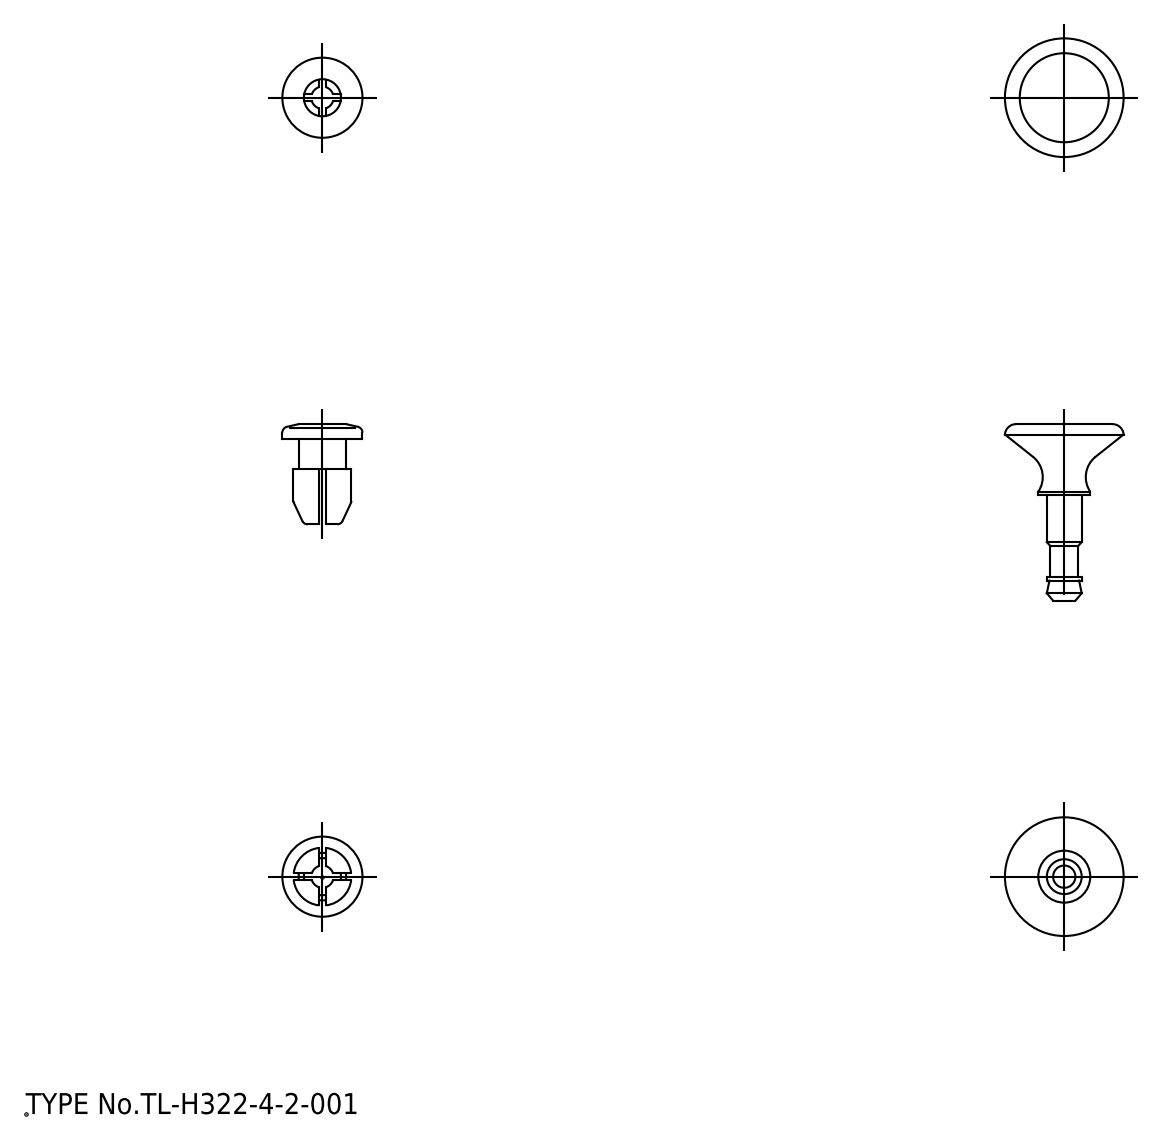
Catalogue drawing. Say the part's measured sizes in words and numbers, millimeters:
The part is named "grommet; plunger". Its 3-D file was written by "spGate 18.9.1 (****-****-****-****) (AUTOMOTIVE_DESIGN)". It is 2 solids with 83 faces: 27 planar, 22 cylindrical and 34 other. Overall it measures 25.8 by 16 by 16 millimeters. Its volume is 1 213 cubic millimeters and its surface area 1 475 square millimeters. Round holes: 1 of diameter 5. Round bosses or shafts: 1 of diameter 10.8, 1 of diameter 7.8, 1 of diameter 7, 1 of diameter 6.4, 1 of diameter 4.7, 1 of diameter 3.8. Partial cylindrical surfaces (rounded edges, fillets, slot ends): 1 of radius 1.5. The main face-to-face distances are 1, 9.5, 14.3, 4.8, 2, 4.1, 8.9, 18.4, 6.1, 2.8.
